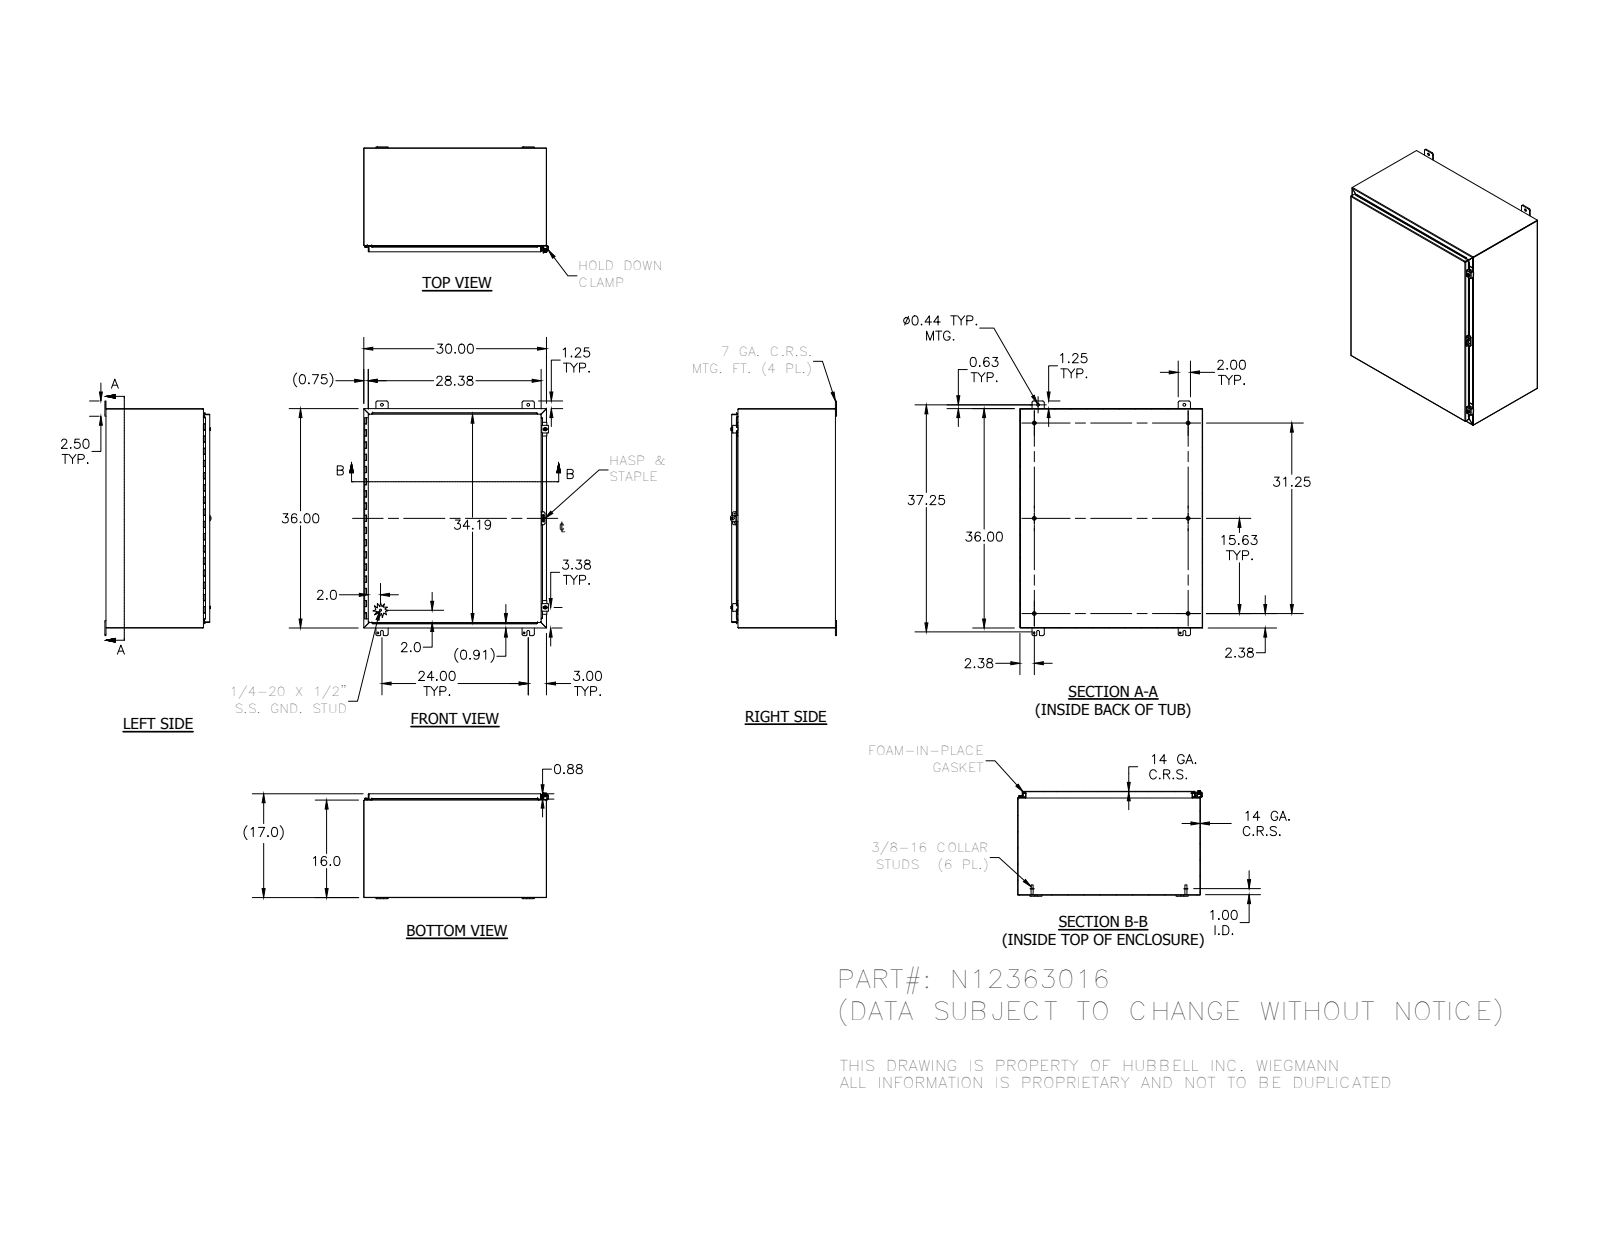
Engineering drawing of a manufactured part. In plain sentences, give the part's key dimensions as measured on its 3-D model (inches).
The part is named "N12363016; 34840; 38413; N123016TB (+8 more)". Its 3-D file was written by "Autodesk Inventor 2012 (AUTOMOTIVE_DESIGN)". It is 31 solids with 982 faces: 581 planar, 298 cylindrical and 103 other. Overall it measures 38.5 by 30.311 by 17.41 inches. Its volume is 359 cubic inches and its surface area 9 512 square inches. Round holes: 4 of diameter 0.313, 4 of diameter 0.438, 3 of diameter 0.11, 2 of diameter 0.211, 2 of diameter 0.281, 2 of diameter 0.3, 1 of diameter 0.125, 1 of diameter 0.156, 1 of diameter 0.5. Round bosses or shafts: 6 of diameter 0.625, 6 of diameter 0.33, 4 of diameter 0.25, 2 of diameter 0.52, 2 of diameter 0.5, 2 of diameter 0.35, 2 of diameter 0.115, 1 of diameter 0.337. Partial cylindrical surfaces (rounded edges, fillets, slot ends): 27 of radius 0.03, 25 of radius 0.125, 25 of radius 0.25, 21 of radius 0.031, 21 of radius 0.105, 13 of radius 0.063, 4 of radius 0.1, 4 of radius 0.141. The main face-to-face distances are 0.074, 16.959, 29.926, 16.885, 17.033, 35.926, 29.852, 30, 35.852, 36. The hole center spacings are 1.593, 24, 36, 43.267, 0.791, 23.357, 24.729, 34.57.
